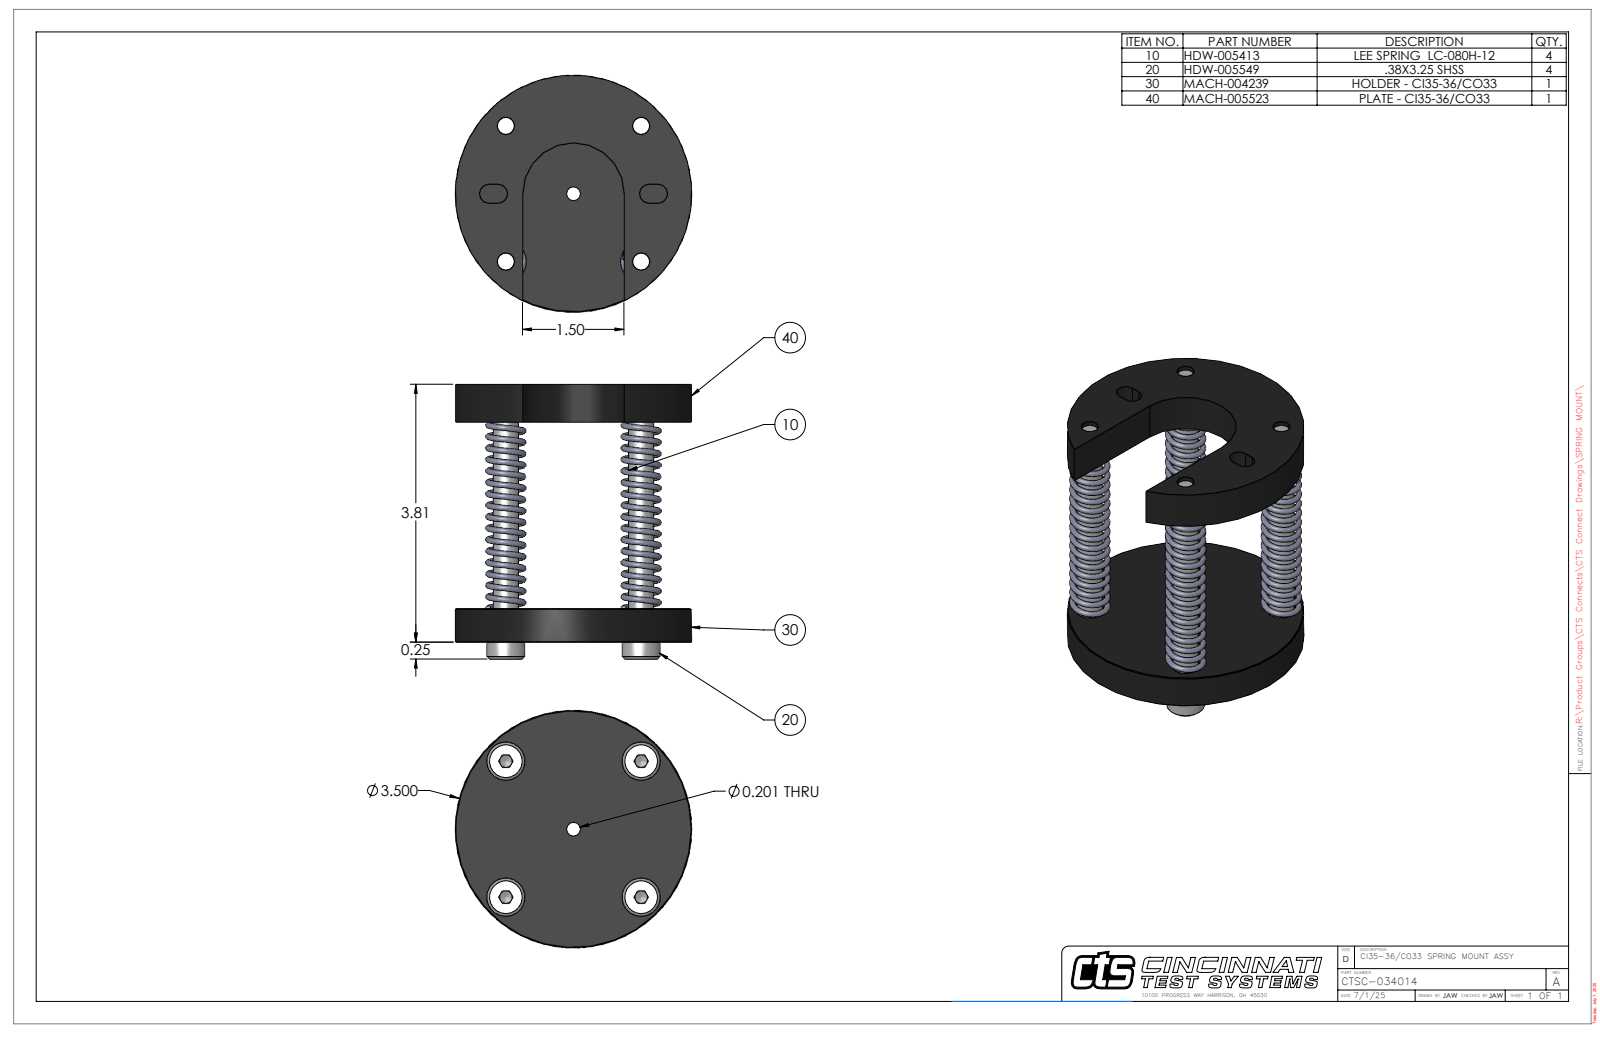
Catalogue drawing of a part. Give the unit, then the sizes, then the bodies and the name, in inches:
Units: inches
Overall size (bounding box): 4.063 × 3.5 × 3.5
Round holes (diameter × count): ⌀0.257 ×4, ⌀0.422 ×4, ⌀0.201 ×1
Round bosses / shafts (diameter × count): ⌀0.562 ×4, ⌀0.373 ×4, ⌀0.352 ×4, ⌀0.313 ×4, ⌀0.237 ×4, ⌀3.5 ×1
Partial cylindrical surfaces — rounded edges, fillets, slot ends (radius × count): R0.141 ×4, R0.75 ×1
Main face-to-face distances: 0.5, 3.25, 2.75, 0.563, 3.313, 3.813, 1.5, 0.25, 4.063, 3.5
Hole centre spacings: 1.414, 2, 2.828
Volume: 10.08 in³ · Surface area: 97.38 in²
Bodies: 10 solids, 228 faces (90 planar, 70 cylindrical, 68 other)
Part name (STEP PRODUCT): MACH-005523 (PLATE - CI35-36,CO33); CTSC-034014 (CI35-36, CO33 SPRING MOUNT); .38 X 3.25LG SHSS_SHSSCREW 0.375x3.25-N; LEE SPRING LC-080H-12 (+1 more)
STEP written by: SolidWorks 2023 (AUTOMOTIVE_DESIGN)
